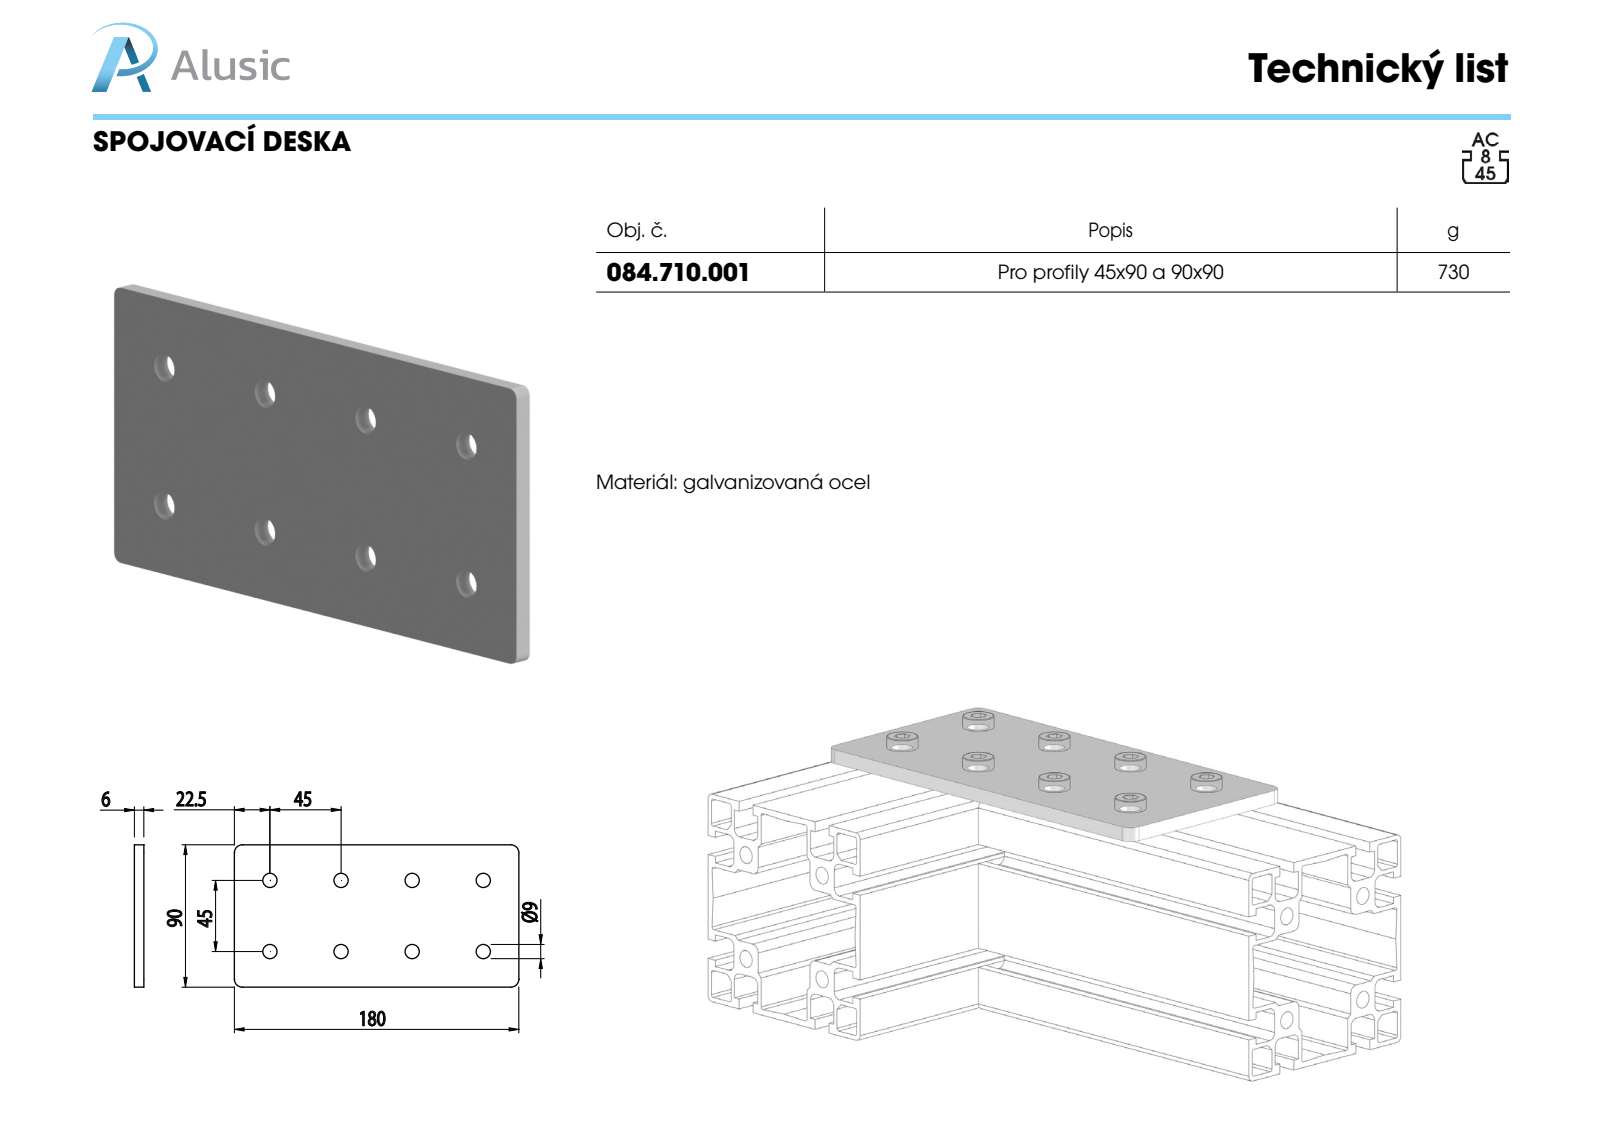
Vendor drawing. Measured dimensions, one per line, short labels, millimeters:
name: 084.710.001
written by: SolidWorks 2011 (CONFIG_CONTROL_DESIGN)
unit: mm
bodies: 1 solid, 26 faces (6 planar, 20 cylindrical, 0 other)
size: 180 × 90 × 6
volume: 94 018 mm³; area: 35 885 mm²
holes: 8× ⌀9
rounds: 4× R5
face distances: 6, 90, 180
hole spacings: 45, 63.64, 90, 100.62, 135, 142.3
